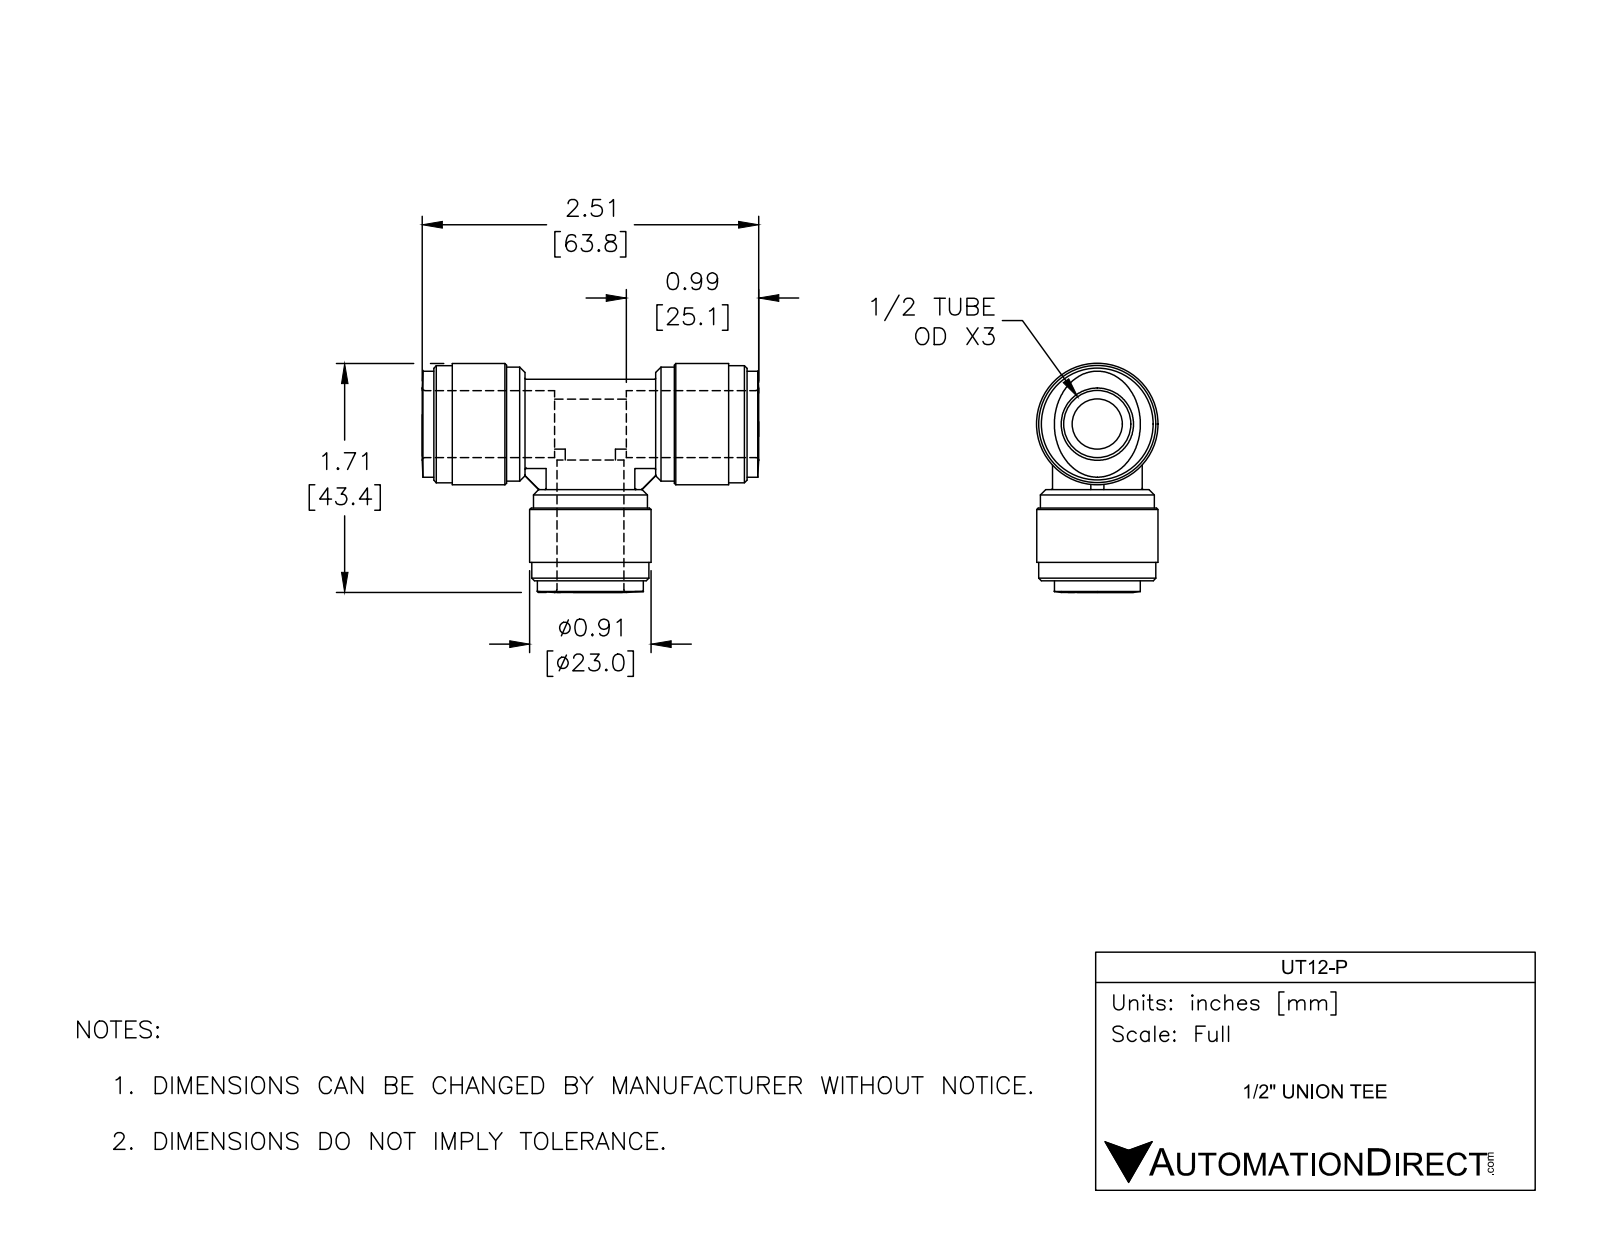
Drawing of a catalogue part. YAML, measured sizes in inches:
part_name: "UT12-P"
step_written_by: "SolidWorks 2017 (AUTOMOTIVE_DESIGN)"
units: inches
bodies: {solids: 1, faces: 96, planar: 20, cylindrical: 32, other: 44}
overall_size: [2.512, 1.709, 0.906]
volume: 1.126
surface_area: 15.84
round_holes:
  - {diameter: 0.374, count: 2}
  - {diameter: 0.5, count: 2}
round_bosses_or_shafts:
  - {diameter: 0.906, count: 2}
  - {diameter: 0.874, count: 2}
  - {diameter: 0.85, count: 2}
  - {diameter: 0.669, count: 2}
face_to_face_distances: [0.681, 1.657, 0.138, 0.543, 0.902, 0.22, 1.437, 0.756, 2.339, 0.764]
